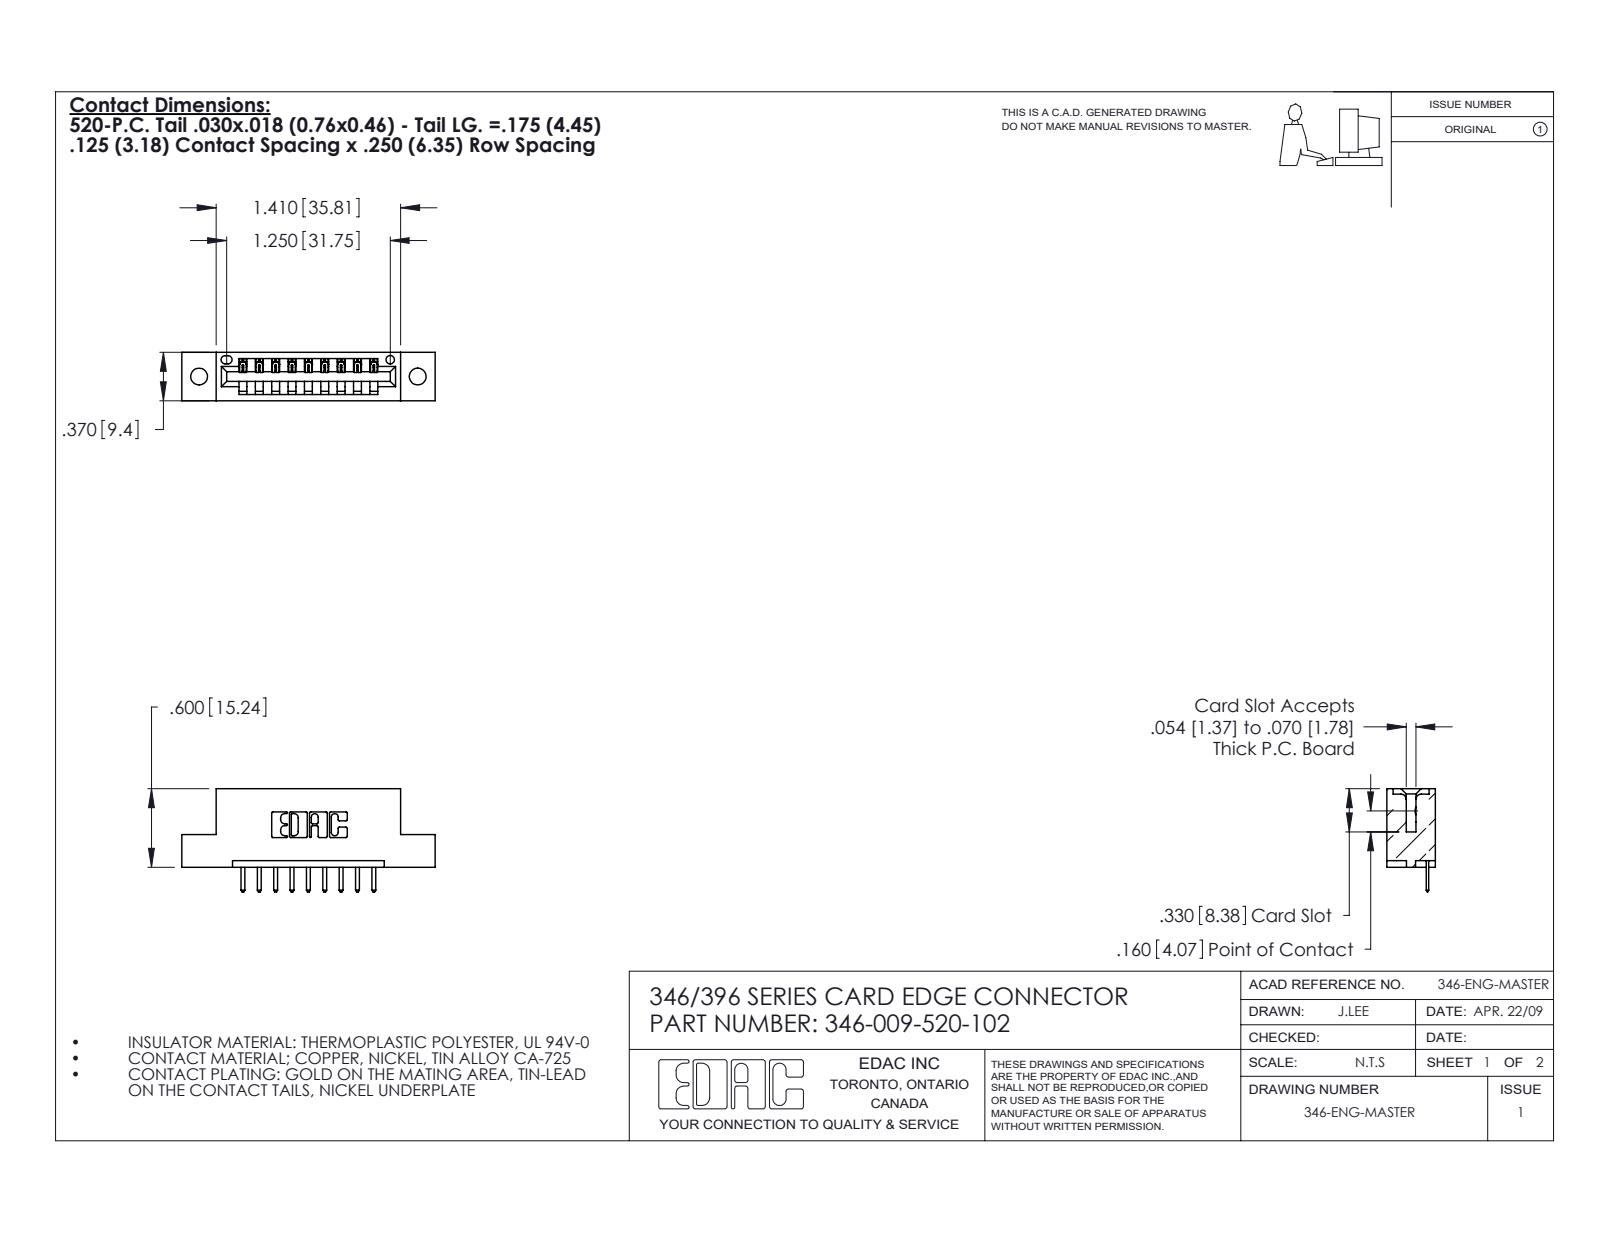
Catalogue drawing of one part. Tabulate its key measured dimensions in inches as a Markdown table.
| quantity | value |
| --- | --- |
| part name | 345-292-001_345-293-120; 346-009-520-102; 346 Part_Flush Mounting Lugs - 0.128 Dia |
| STEP written by | SolidWorks 2020 (CONFIG_CONTROL_DESIGN) |
| units | inches |
| bodies | 10 solids, 680 faces (454 planar, 226 cylindrical, 0 other) |
| overall size | 1.935 × 0.788 × 0.37 |
| volume | 0.269 in³ |
| surface area | 7.446 in² |
| round holes (diameter × count) | 0.128 × 2, 0.064 × 1 |
| partial cylindrical surfaces (radius × count) | 0.01 × 22, 0.01 × 20, 0.006 × 18, 0.007 × 6, 0.031 × 6, 0.026 × 3, 0.031 × 2, 0.04 × 2 |
| main face-to-face distances | 0.25, 0.37, 0.048, 0.322, 0.148, 0.222, 0.1, 0.174, 0.125, 0.5 |
| hole center spacings | 0.246, 1.465, 1.67 |
